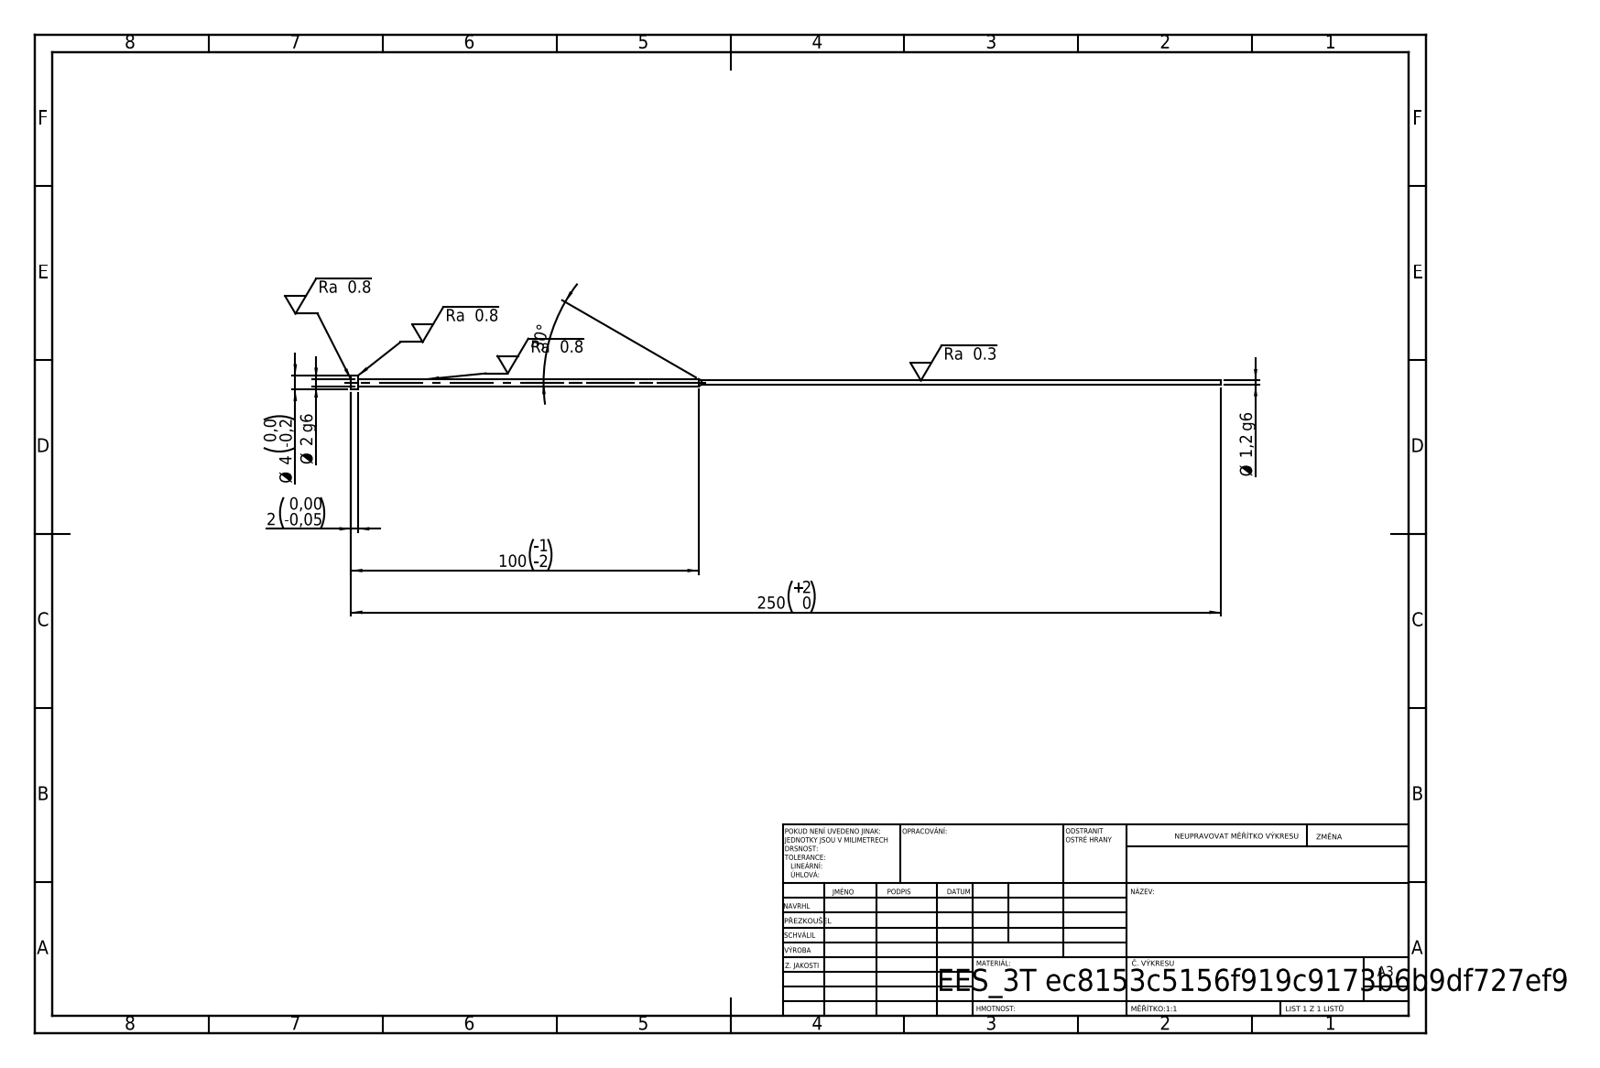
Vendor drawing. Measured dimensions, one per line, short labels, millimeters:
written by: SolidWorks 2019 (CONFIG_CONTROL_DESIGN)
unit: mm
bodies: 1 solid, 11 faces (3 planar, 6 cylindrical, 2 other)
size: 250 × 4 × 4
volume: 503 mm³; area: 1 231 mm²
bosses: 1× ⌀4, 1× ⌀2, 1× ⌀1.2
face distances: 2, 248, 250
